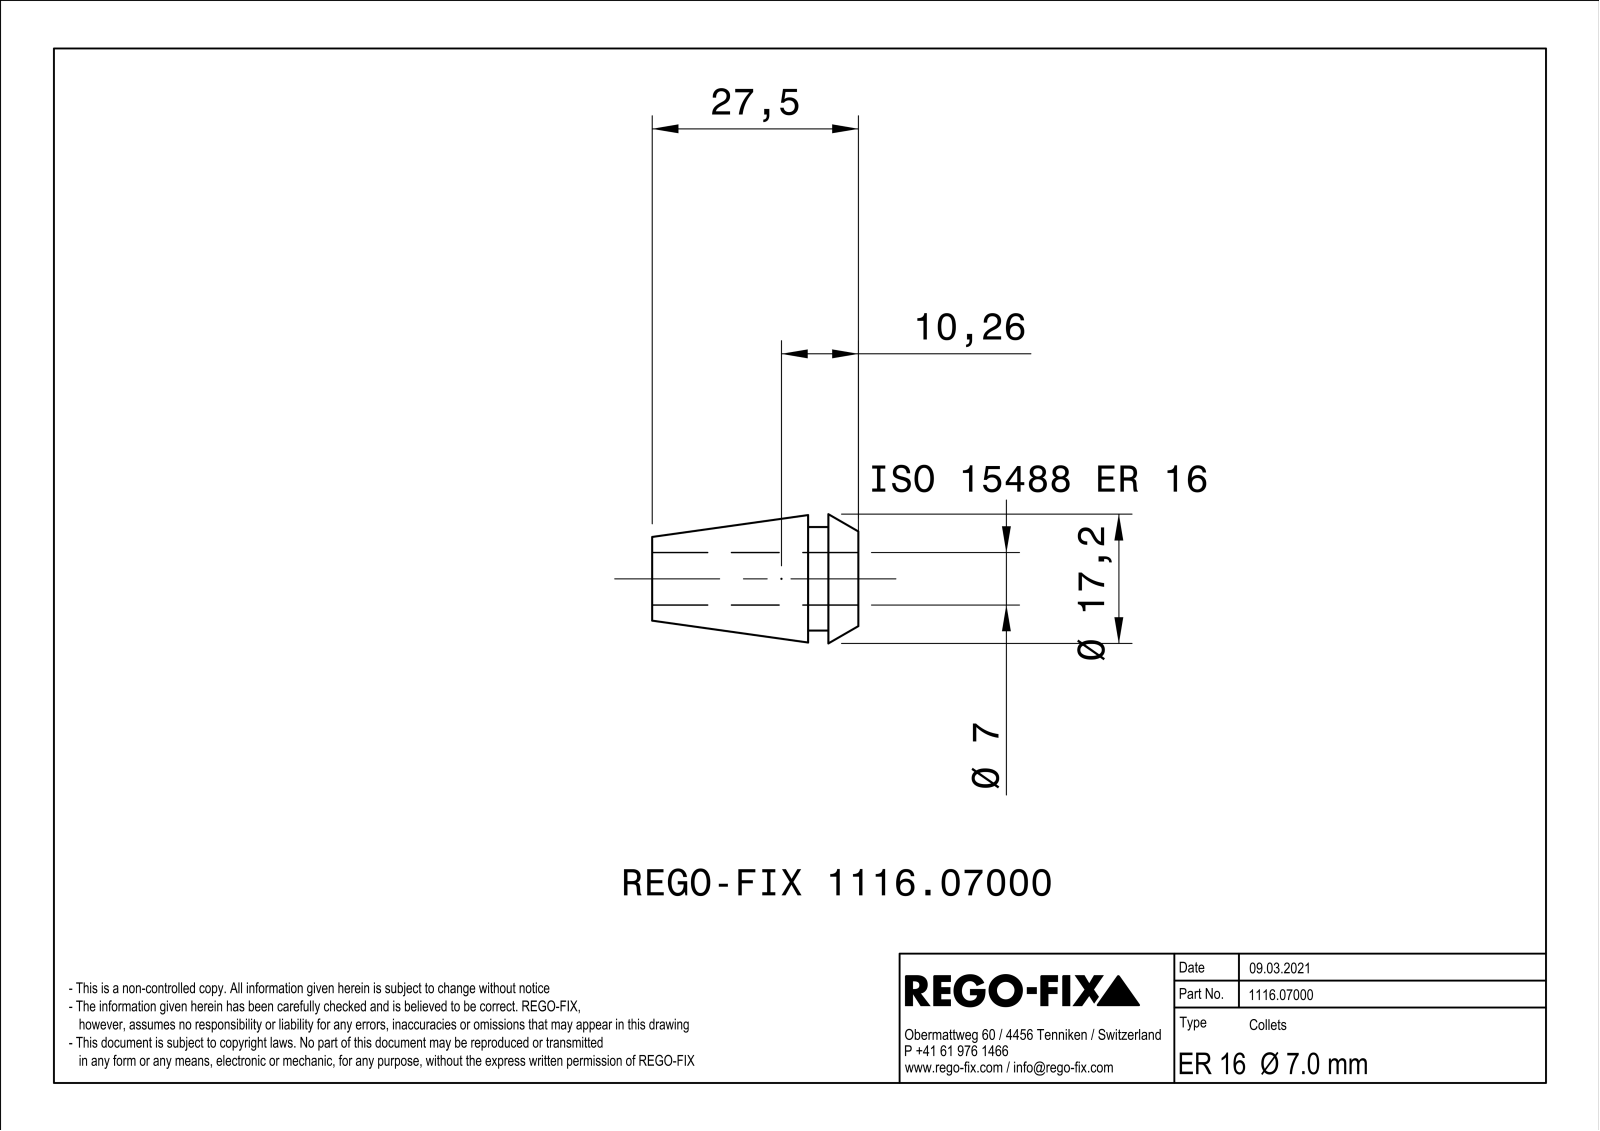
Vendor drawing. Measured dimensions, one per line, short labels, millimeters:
name: NOCUT
written by: SIEMENS PLM Software Solid Edge ST10 (AUTOMOTIVE_DESIGN)
unit: mm
bodies: 1 solid, 153 faces (72 planar, 25 cylindrical, 56 other)
size: 27.5 × 17.24 × 17.24
volume: 2 497 mm³; area: 4 467 mm²
holes: 1× ⌀7
bosses: 1× ⌀13.8
rounds: 8× R0.3
face distances: 0.6, 4, 6.7, 2.7, 27.5, 23.5, 20.8
